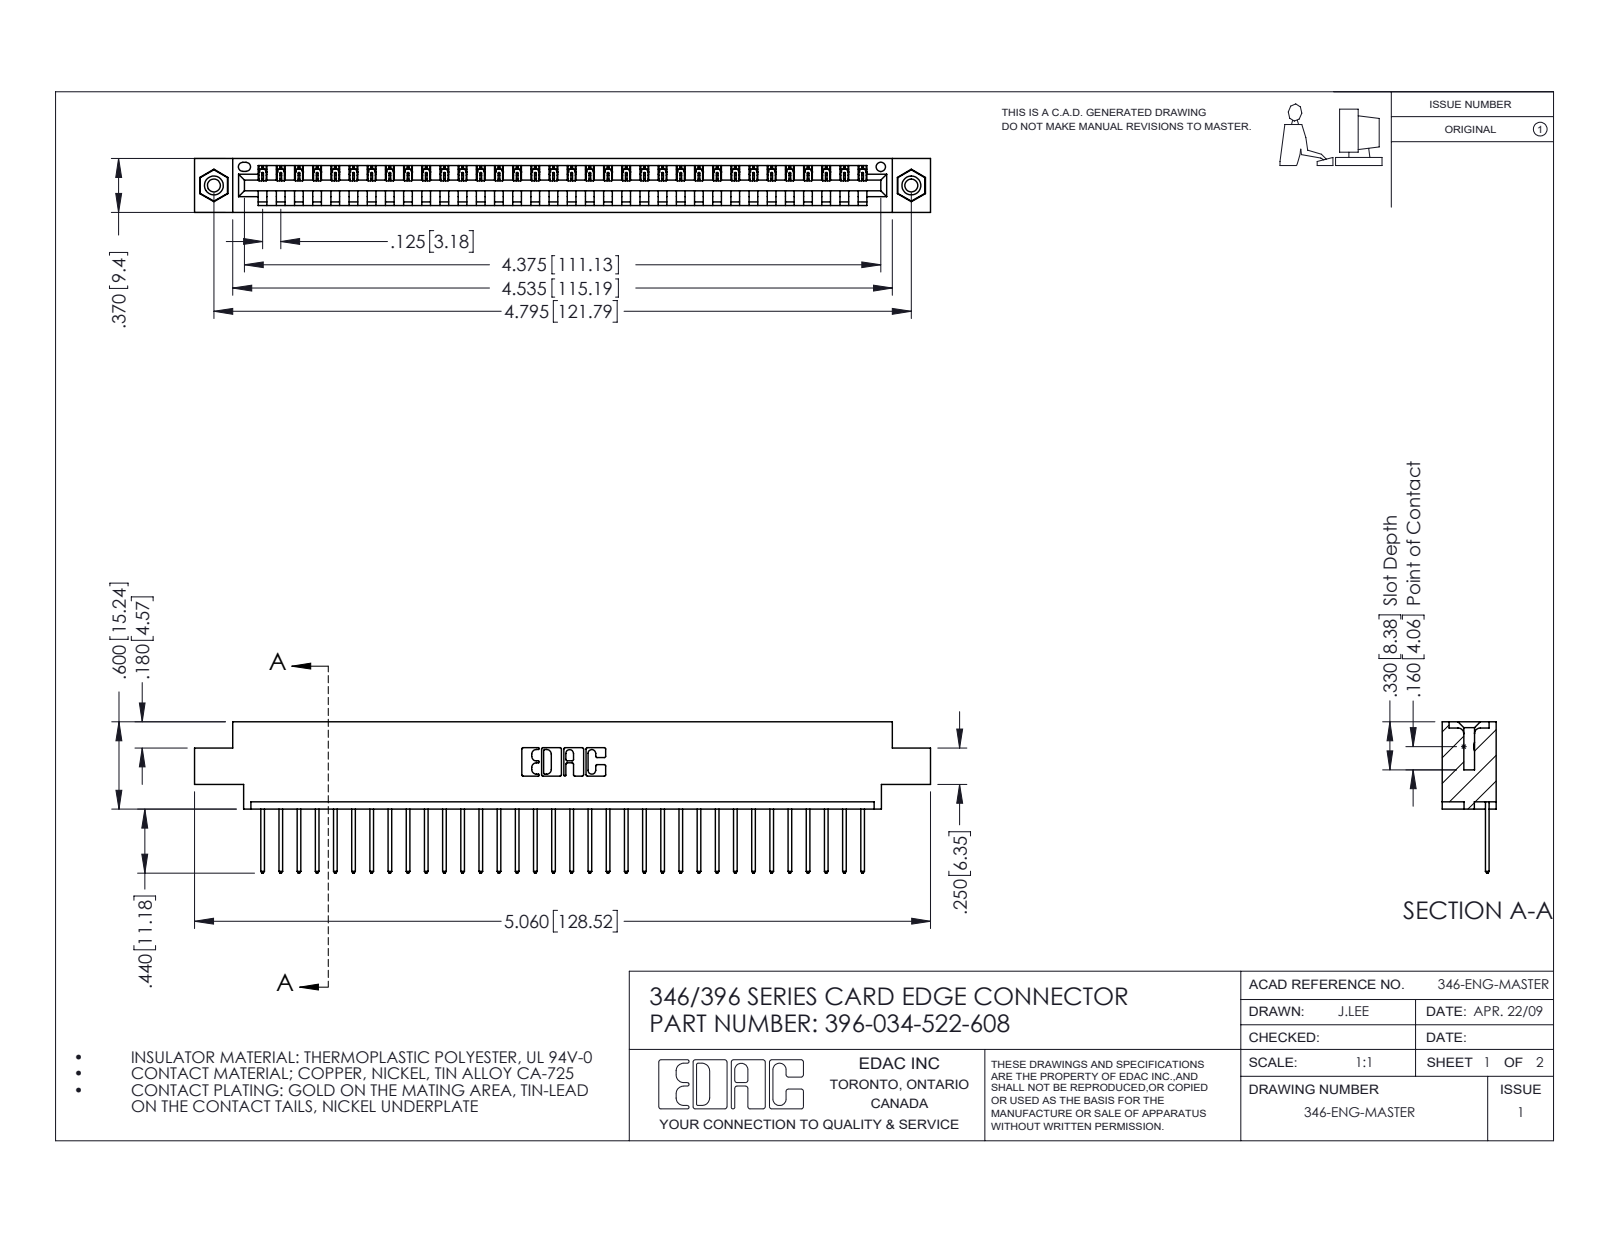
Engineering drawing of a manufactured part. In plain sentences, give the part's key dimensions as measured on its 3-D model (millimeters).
The part is named "396-034-522-608; 345-250-001_345-250-003-102; 346 Part_0.170 Offset - 0.156 Dia-TI; 345-292-001_345-293-122". Its 3-D file was written by "SolidWorks 2016 (CONFIG_CONTROL_DESIGN)". It is 37 solids with 2158 faces: 1472 planar, 670 cylindrical and 16 other. Overall it measures 128.5 by 26.4 by 9.4 millimeters. Its volume is 12 100 cubic millimeters and its surface area 15 340 square millimeters. Round holes: 2 of diameter 2.3, 2 of diameter 3.2, 2 of diameter 4, 1 of diameter 1.6. Round bosses or shafts: 2 of diameter 3.9. Partial cylindrical surfaces (rounded edges, fillets, slot ends): 68 of radius 0.2, 68 of radius 0.3, 22 of radius 0.3, 6 of radius 0.2, 6 of radius 0.8, 3 of radius 0.7, 2 of radius 0.8, 2 of radius 1. The main face-to-face distances are 1.2, 8.2, 9.4, 6.4, 1.8, 7.6, 0.6, 5.6, 3.8, 2.5. The hole center spacings are 6.2, 116.5, 121.8.
